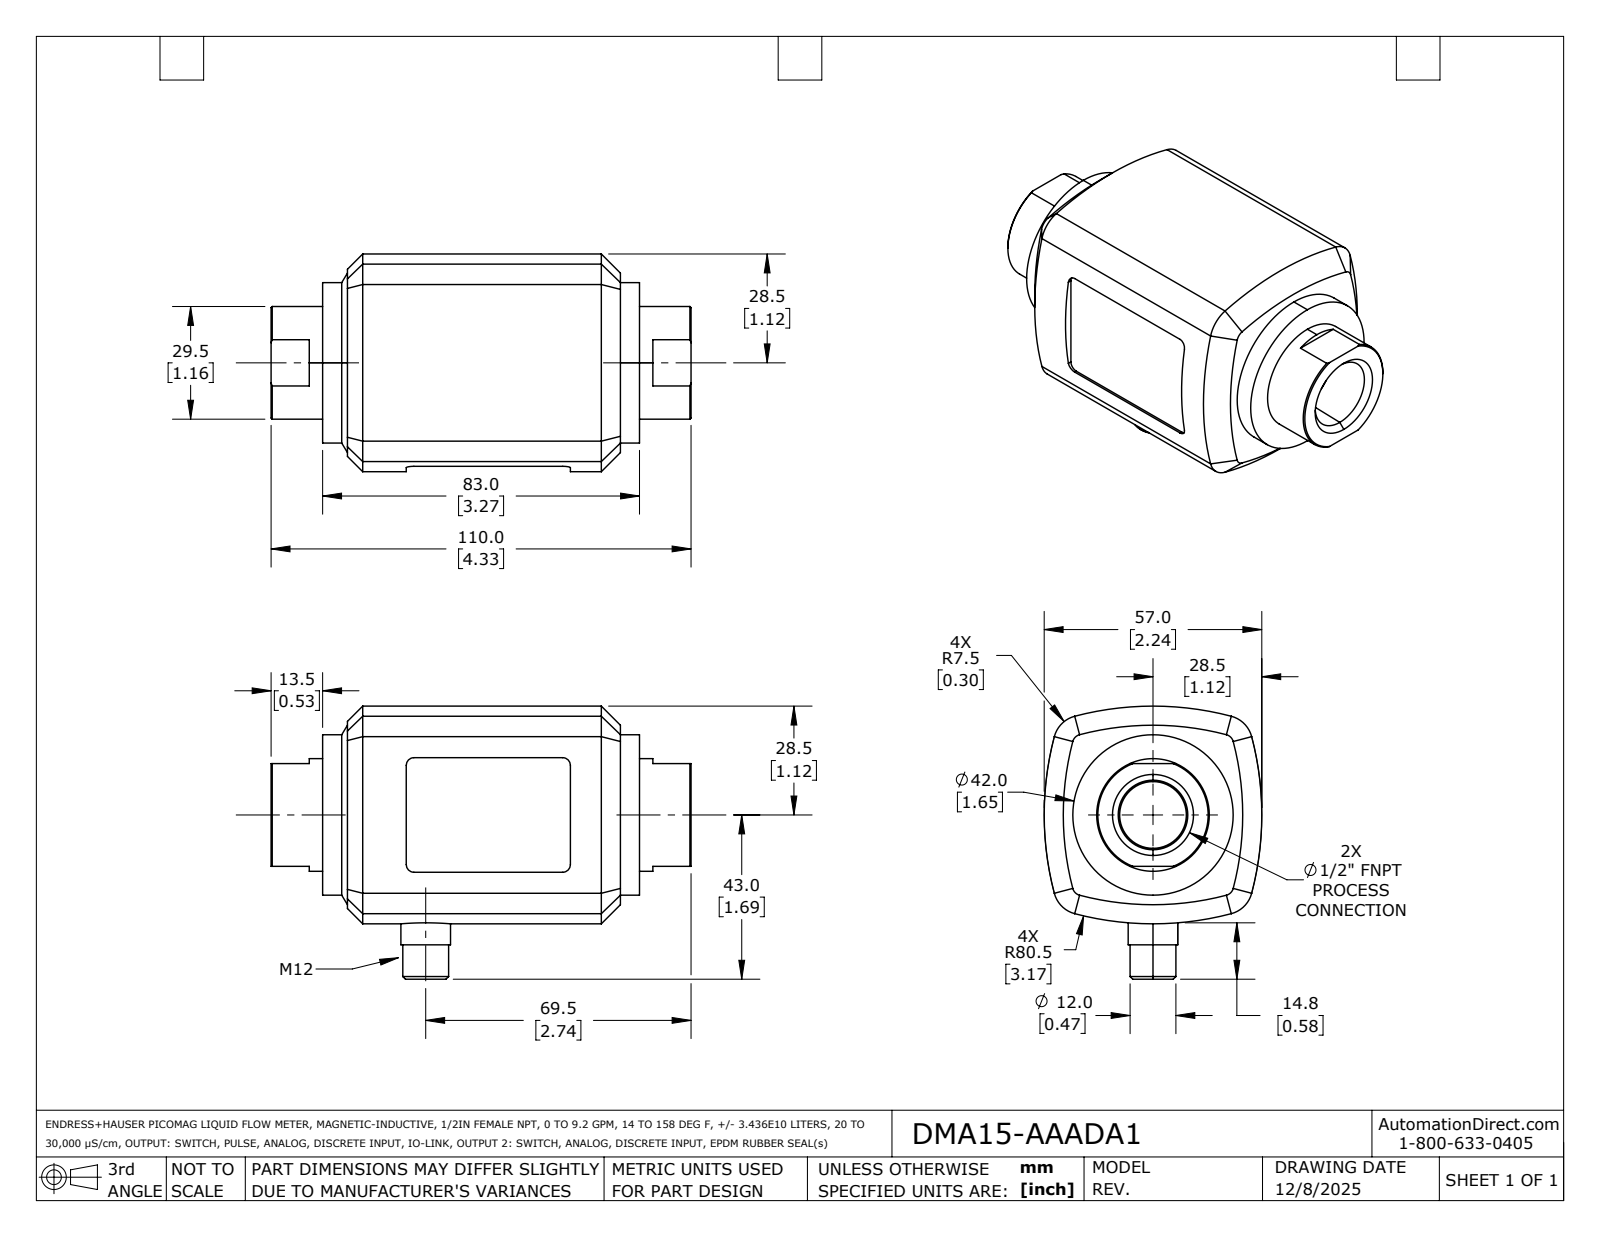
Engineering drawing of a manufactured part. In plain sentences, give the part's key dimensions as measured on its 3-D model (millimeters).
The part is named "DMA15-AAADA1". Its 3-D file was written by "SolidWorks 2024 (AUTOMOTIVE_DESIGN)". It is 1 solid with 82 faces: 24 planar, 26 cylindrical and 32 other. Overall it measures 110 by 71.5 by 57 millimeters. Its volume is 231 887 cubic millimeters and its surface area 25 046 square millimeters. Round holes: 1 of diameter 9.7. Round bosses or shafts: 1 of diameter 42, 1 of diameter 29.5, 1 of diameter 13, 1 of diameter 12. Partial cylindrical surfaces (rounded edges, fillets, slot ends): 4 of radius 2, 4 of radius 7.5, 4 of radius 80.5. The main face-to-face distances are 83, 78, 5, 13.5, 96.5, 13.57, 96.43, 82.93, 6.5, 71.5.
